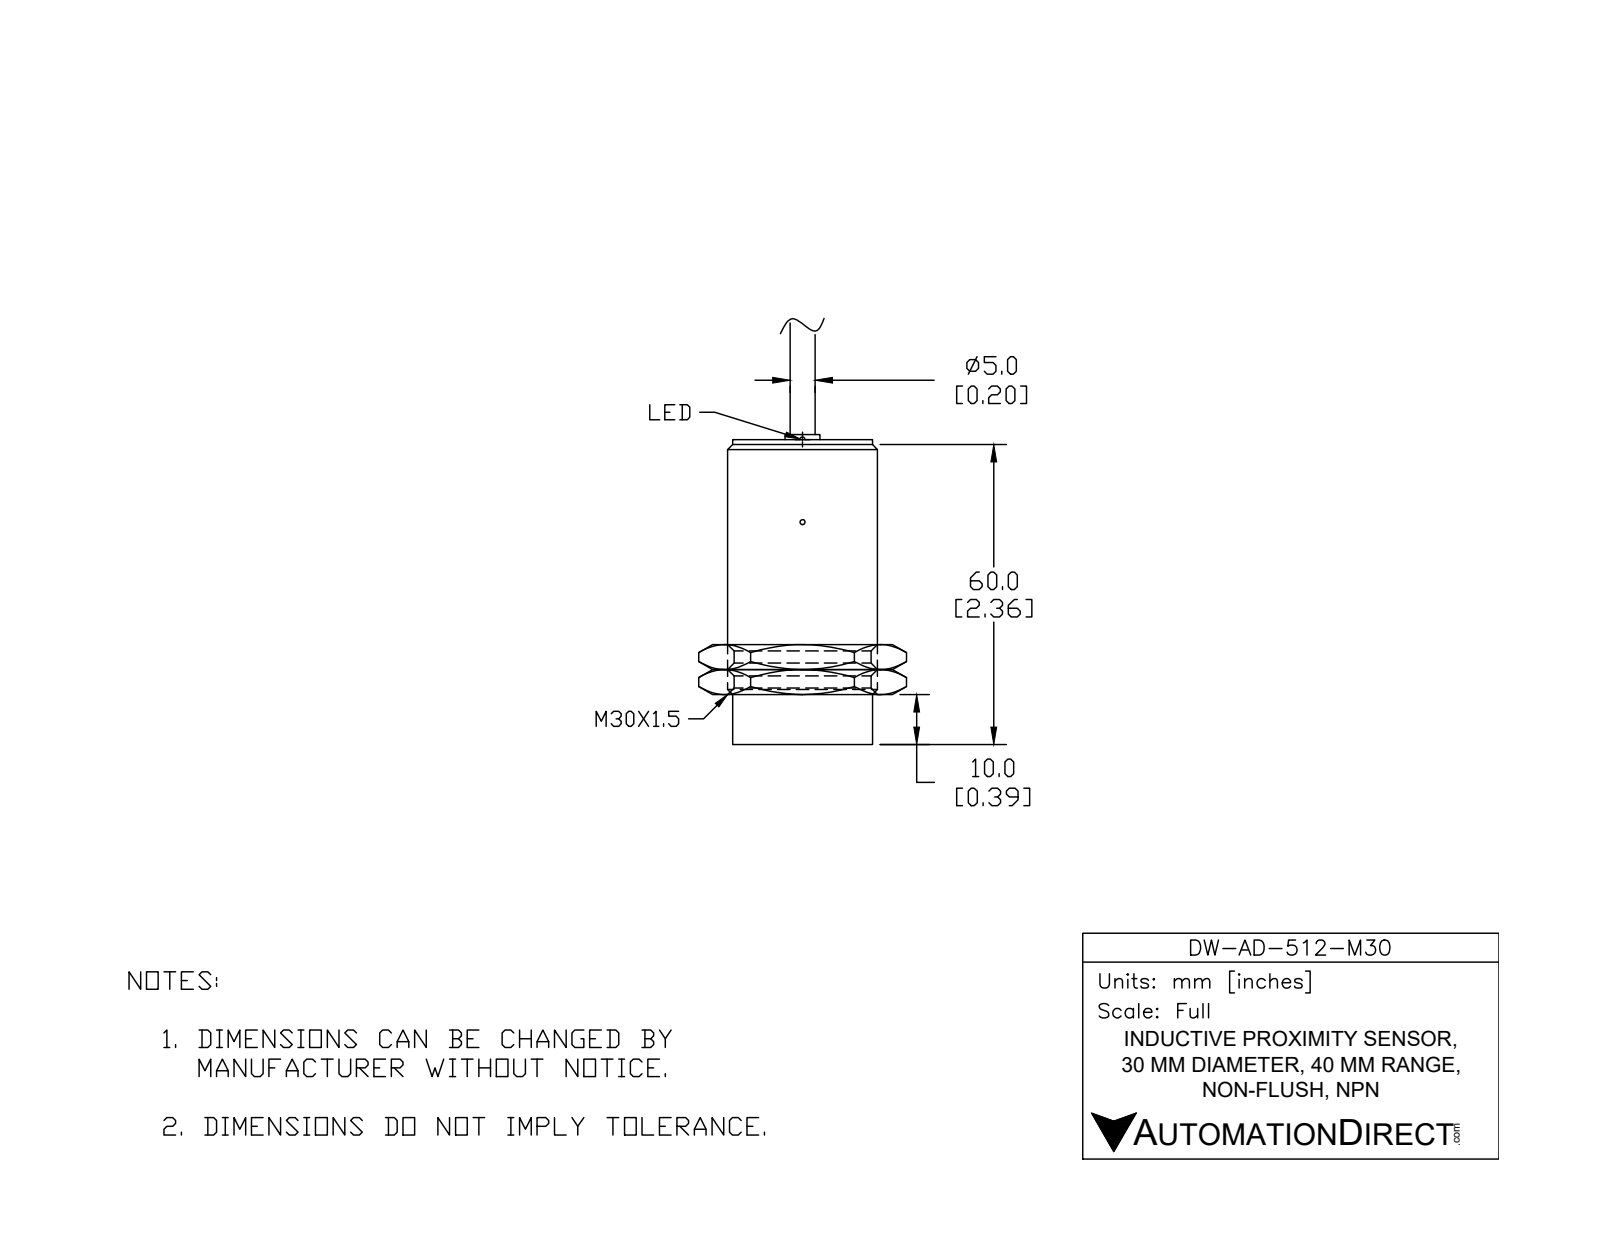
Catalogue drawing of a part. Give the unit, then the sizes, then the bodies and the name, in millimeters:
Units: millimetres
Overall size (bounding box): 88 × 30 × 30
Round bosses / shafts (diameter × count): ⌀30 ×1, ⌀27.5 ×1, ⌀10.5 ×1, ⌀5 ×1
Main face-to-face distances: 10, 61, 51, 61.7, 51.8, 0.8, 88, 78, 27, 26.2
Volume: 42 540 mm³ · Surface area: 8 606 mm²
Bodies: 2 solids, 16 faces (6 planar, 4 cylindrical, 6 other)
Part name (STEP PRODUCT): DW-AD-512-M30
STEP written by: SolidWorks 2017 (AUTOMOTIVE_DESIGN)
